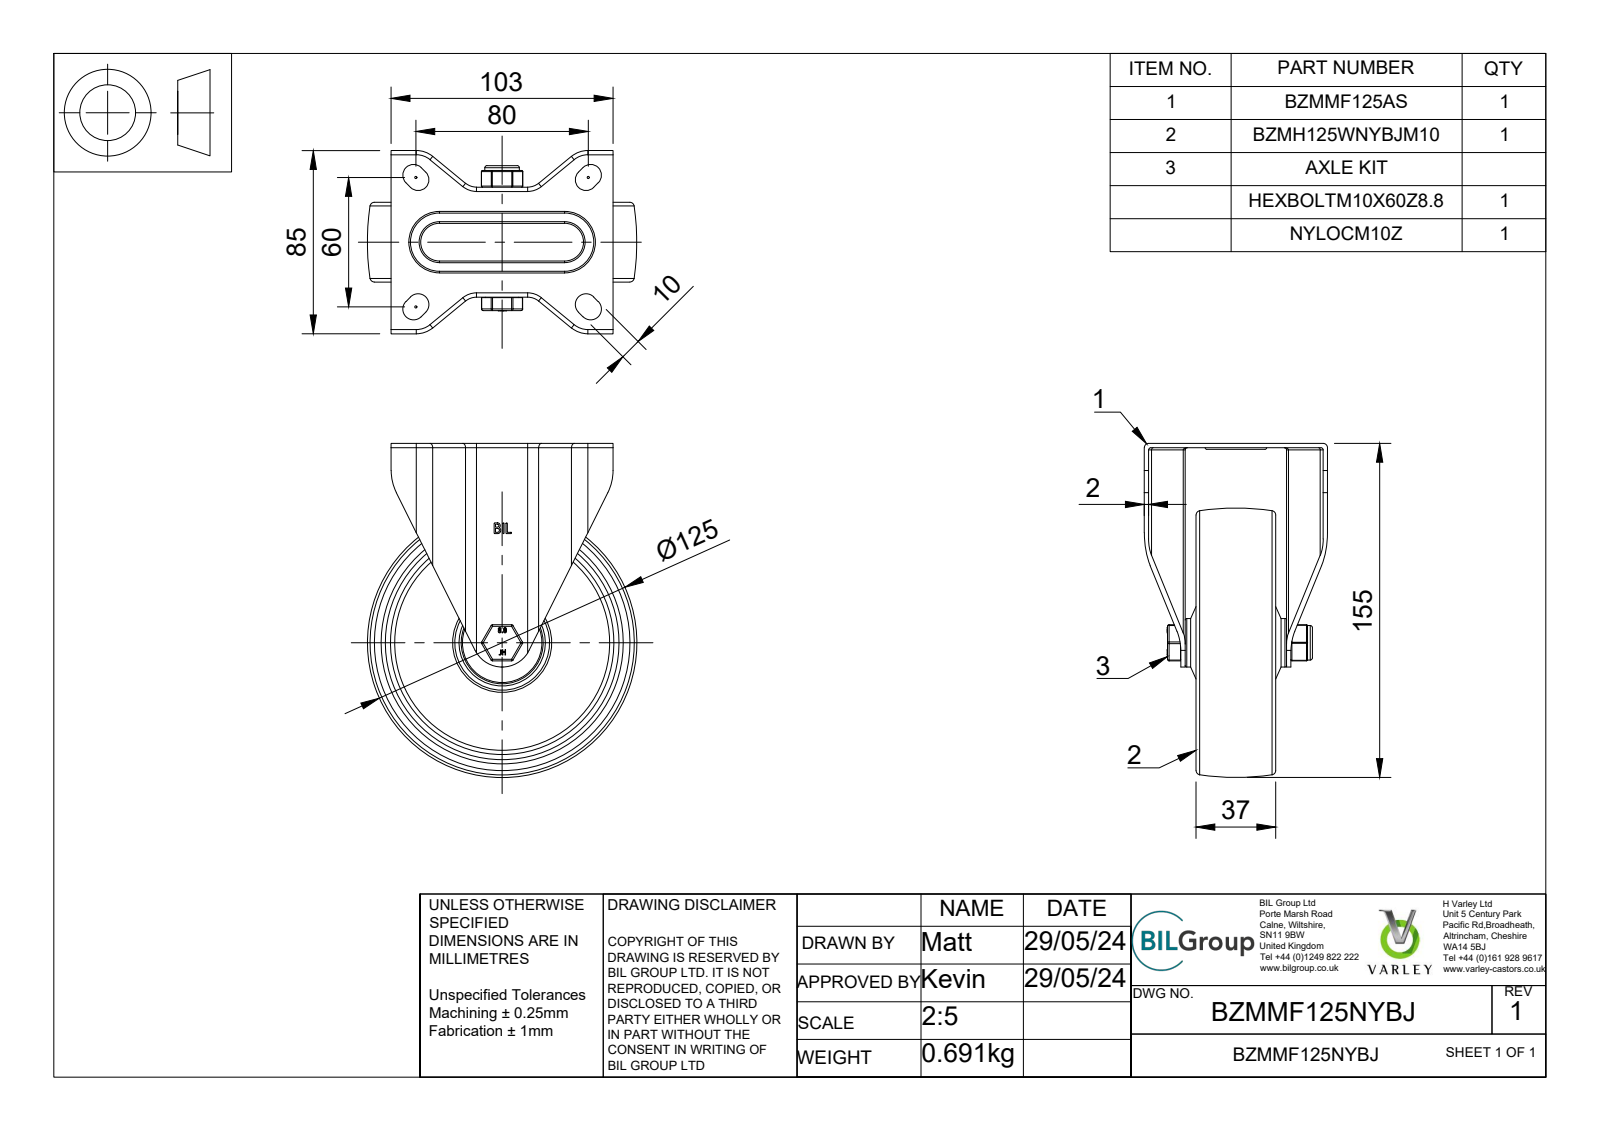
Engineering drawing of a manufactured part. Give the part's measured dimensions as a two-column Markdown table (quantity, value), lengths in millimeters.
| quantity | value |
| --- | --- |
| part name | BZMMF125NYBJ v4; BZMMF125AS - 47 v2; ZINC PLATED, PRESSED STEEL BRACKET; BZMH125WNYBJM10 v1 (+7 more) |
| STEP written by | Autodesk Translation Framework v13.14.0.145 (AUTOMOTIVE_DESIGN) |
| units | millimeters |
| bodies | 20 solids, 773 faces (282 planar, 201 cylindrical, 290 other) |
| overall size | 155 × 125 × 85 |
| volume | 257 652 mm³ |
| surface area | 122 340 mm² |
| round holes (diameter × count) | 10 × 1, 10.2 × 1, 12 × 1, 15 × 1, 20 × 1, 22.5 × 1, 25 × 1, 30 × 1, 31 × 1, 32 × 1, 35 × 1, 36 × 1 |
| round bosses / shafts (diameter × count) | 44 × 1, 38 × 1, 30.5 × 1, 28 × 1, 23 × 1, 19 × 1, 18 × 1, 16 × 1 |
| partial cylindrical surfaces (radius × count) | 0.75 × 20, 0.5 × 18, 1 × 8, 2 × 8, 5 × 8, 12 × 5, 4 × 4, 6 × 4 |
| main face-to-face distances | 2, 22, 7, 20, 29, 27, 18.84, 49, 15, 44 |
